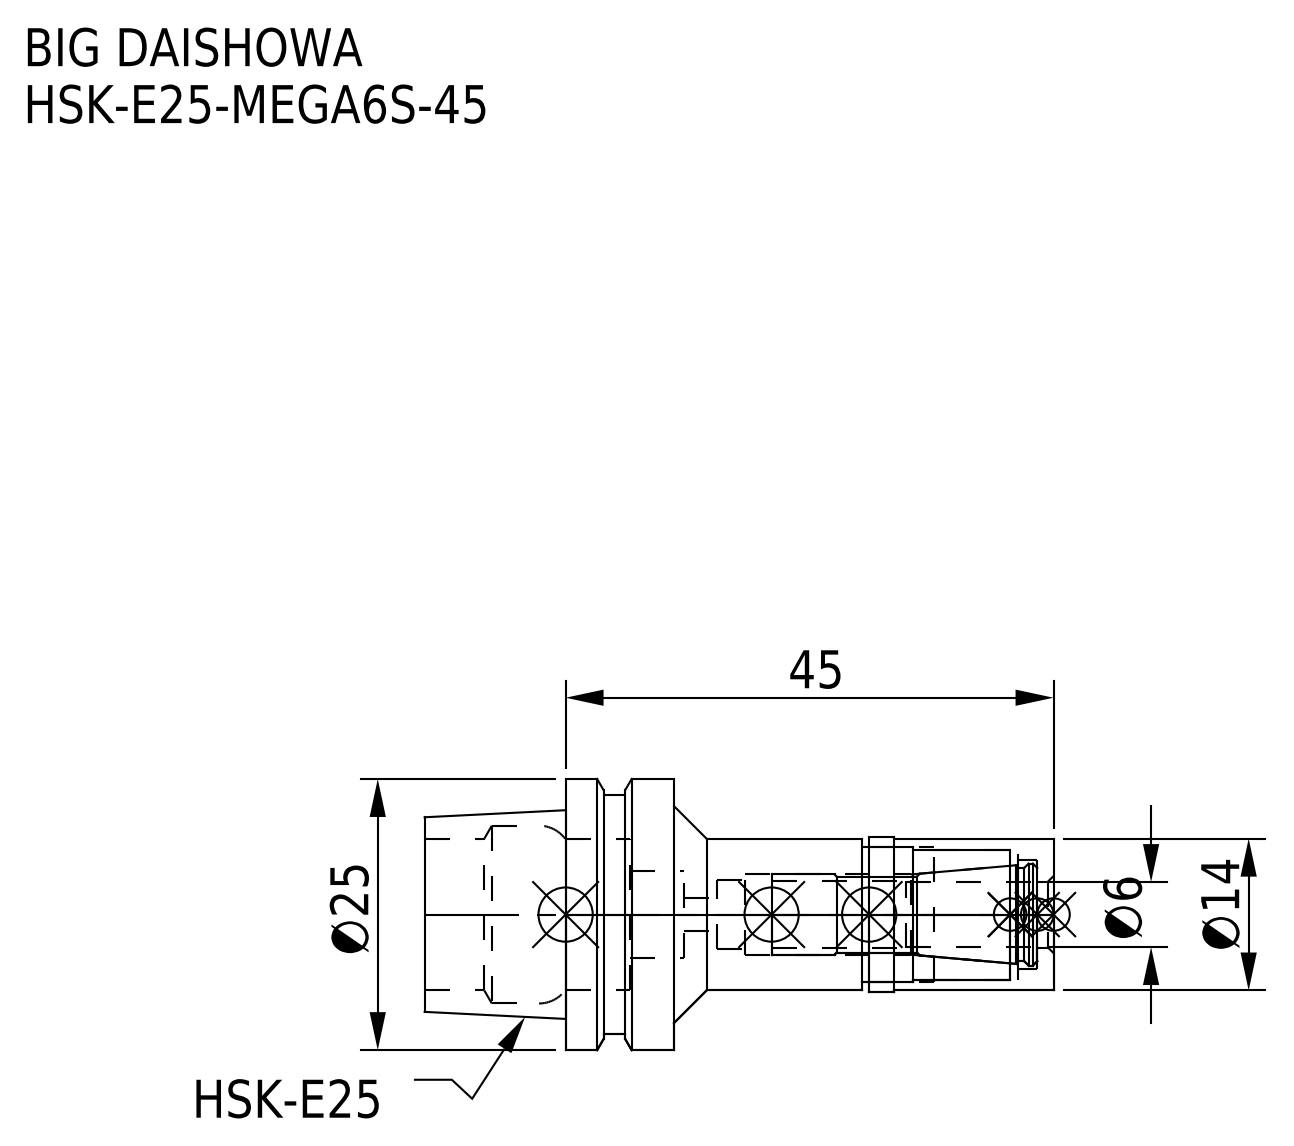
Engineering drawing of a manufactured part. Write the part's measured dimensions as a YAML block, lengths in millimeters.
part_name: "HSK-E25-MEGA6S-45_1.stp; HSK-E25-MEGA6S-45-060.stp; HSK-E25-MEGA6S-45-060-FreeParts; HE25MS06045-060_ASM.stp (+3 more)"
step_written_by: "SolidWorks 2019 (CONFIG_CONTROL_DESIGN)"
units: millimeters
bodies: {solids: 2, faces: 74, planar: 18, cylindrical: 40, other: 16}
overall_size: [58, 25, 25]
volume: 8718
surface_area: 7157
round_holes:
  - {diameter: 3, count: 1}
  - {diameter: 6.1, count: 1}
  - {diameter: 6.4, count: 1}
  - {diameter: 7.4, count: 1}
  - {diameter: 8, count: 1}
  - {diameter: 10, count: 1}
  - {diameter: 12, count: 1}
  - {diameter: 12.5, count: 1}
  - {diameter: 14, count: 1}
  - {diameter: 16.4, count: 1}
round_bosses_or_shafts:
  - {diameter: 25, count: 1}
  - {diameter: 22, count: 1}
  - {diameter: 14.3, count: 1}
face_to_face_distances: [10, 13, 45, 35, 39.05, 4.05, 5.95, 58, 23, 18.95]
